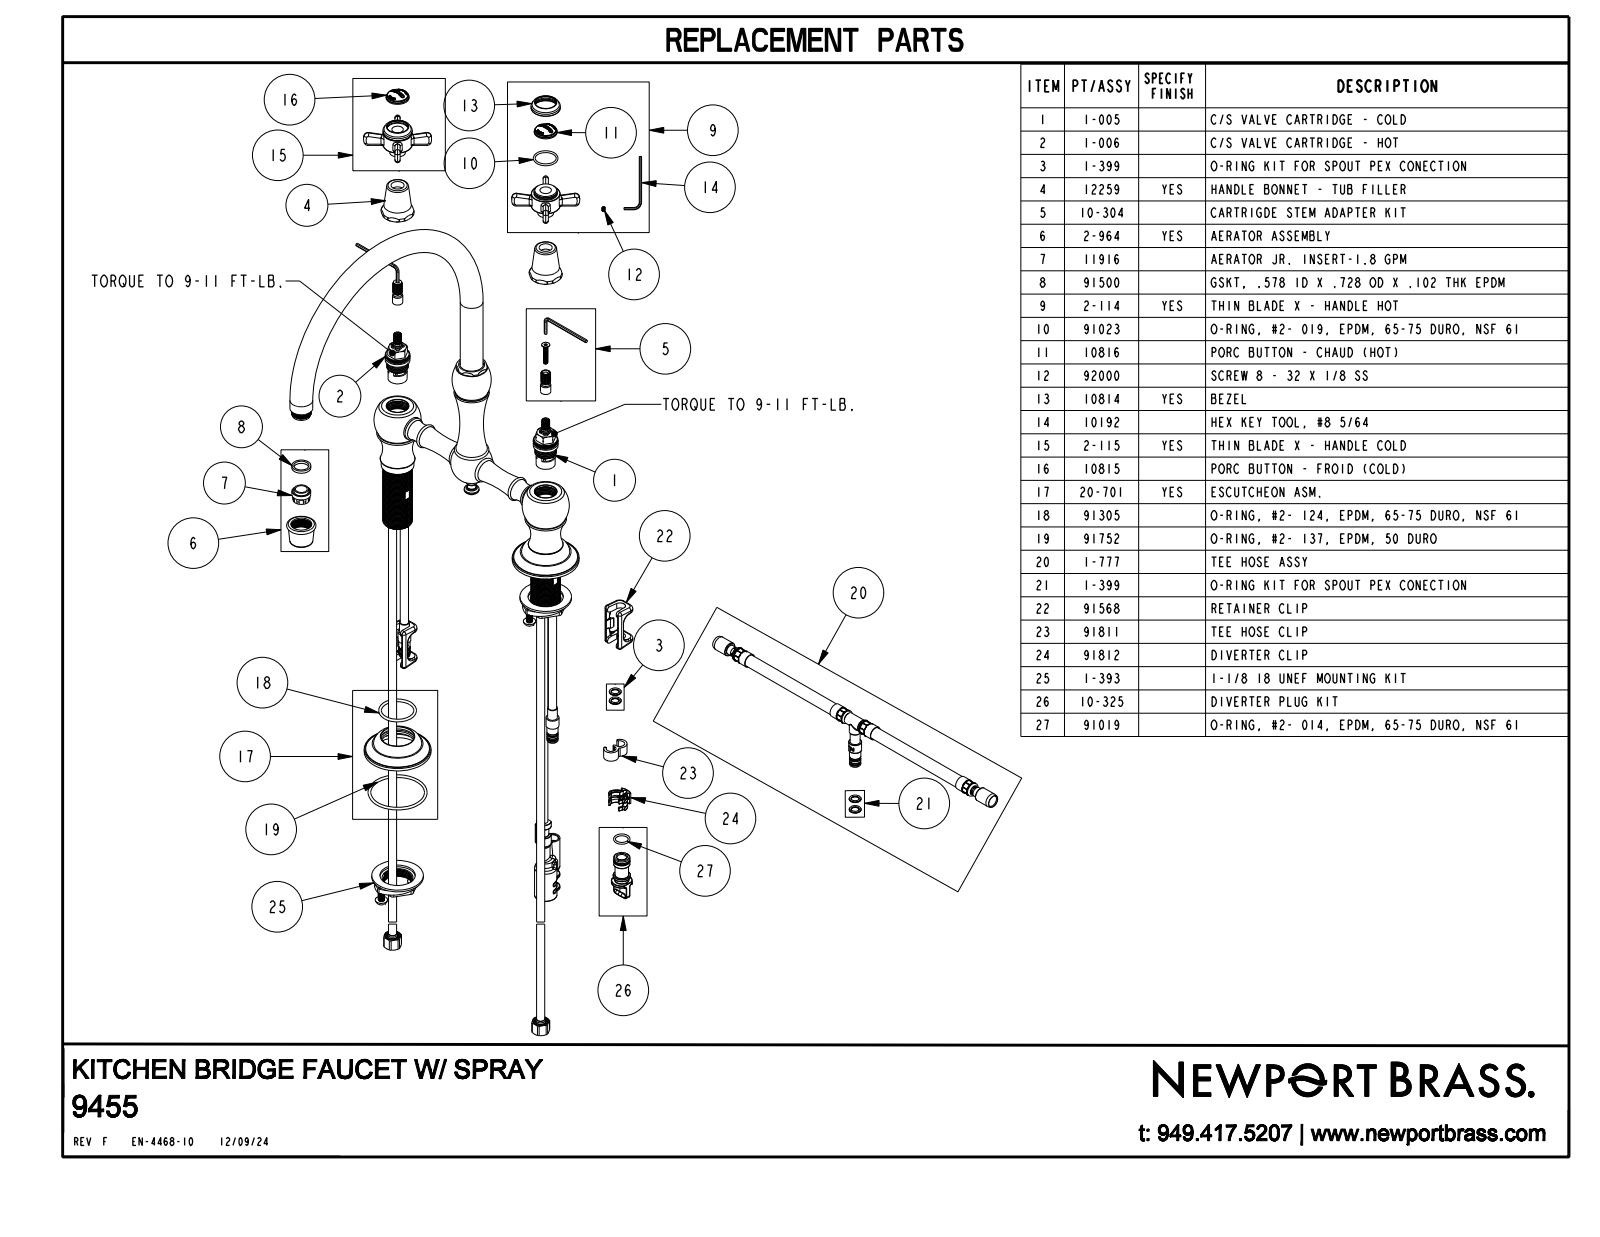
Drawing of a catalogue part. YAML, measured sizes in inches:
part_name: "9455"
step_written_by: "CREO PARAMETRIC BY PTC INC, 2018400 (AUTOMOTIVE_DESIGN)"
units: inches
bodies: {solids: 3, faces: 1093, planar: 449, cylindrical: 314, other: 330}
overall_size: [15.154, 10.735, 10.35]
volume: 34.6
surface_area: 158.7
round_holes:
  - {diameter: 0.9, count: 1}
round_bosses_or_shafts:
  - {diameter: 2.35, count: 2}
  - {diameter: 1.115, count: 2}
  - {diameter: 1.1, count: 2}
  - {diameter: 0.89, count: 2}
  - {diameter: 0.875, count: 2}
  - {diameter: 0.603, count: 2}
  - {diameter: 0.562, count: 1}
  - {diameter: 0.405, count: 1}
partial_cylinders:
  - {radius: 0.011, count: 28}
  - {radius: 0.1, count: 25}
  - {radius: 0.025, count: 17}
  - {radius: 0.006, count: 14}
  - {radius: 0.005, count: 10}
  - {radius: 0.015, count: 10}
  - {radius: 0.006, count: 8}
  - {radius: 0.014, count: 8}
face_to_face_distances: [0.2, 5.656, 4.89, 0.37, 4.52, 5.456, 5.856, 5.47, 0.95, 0.58]
